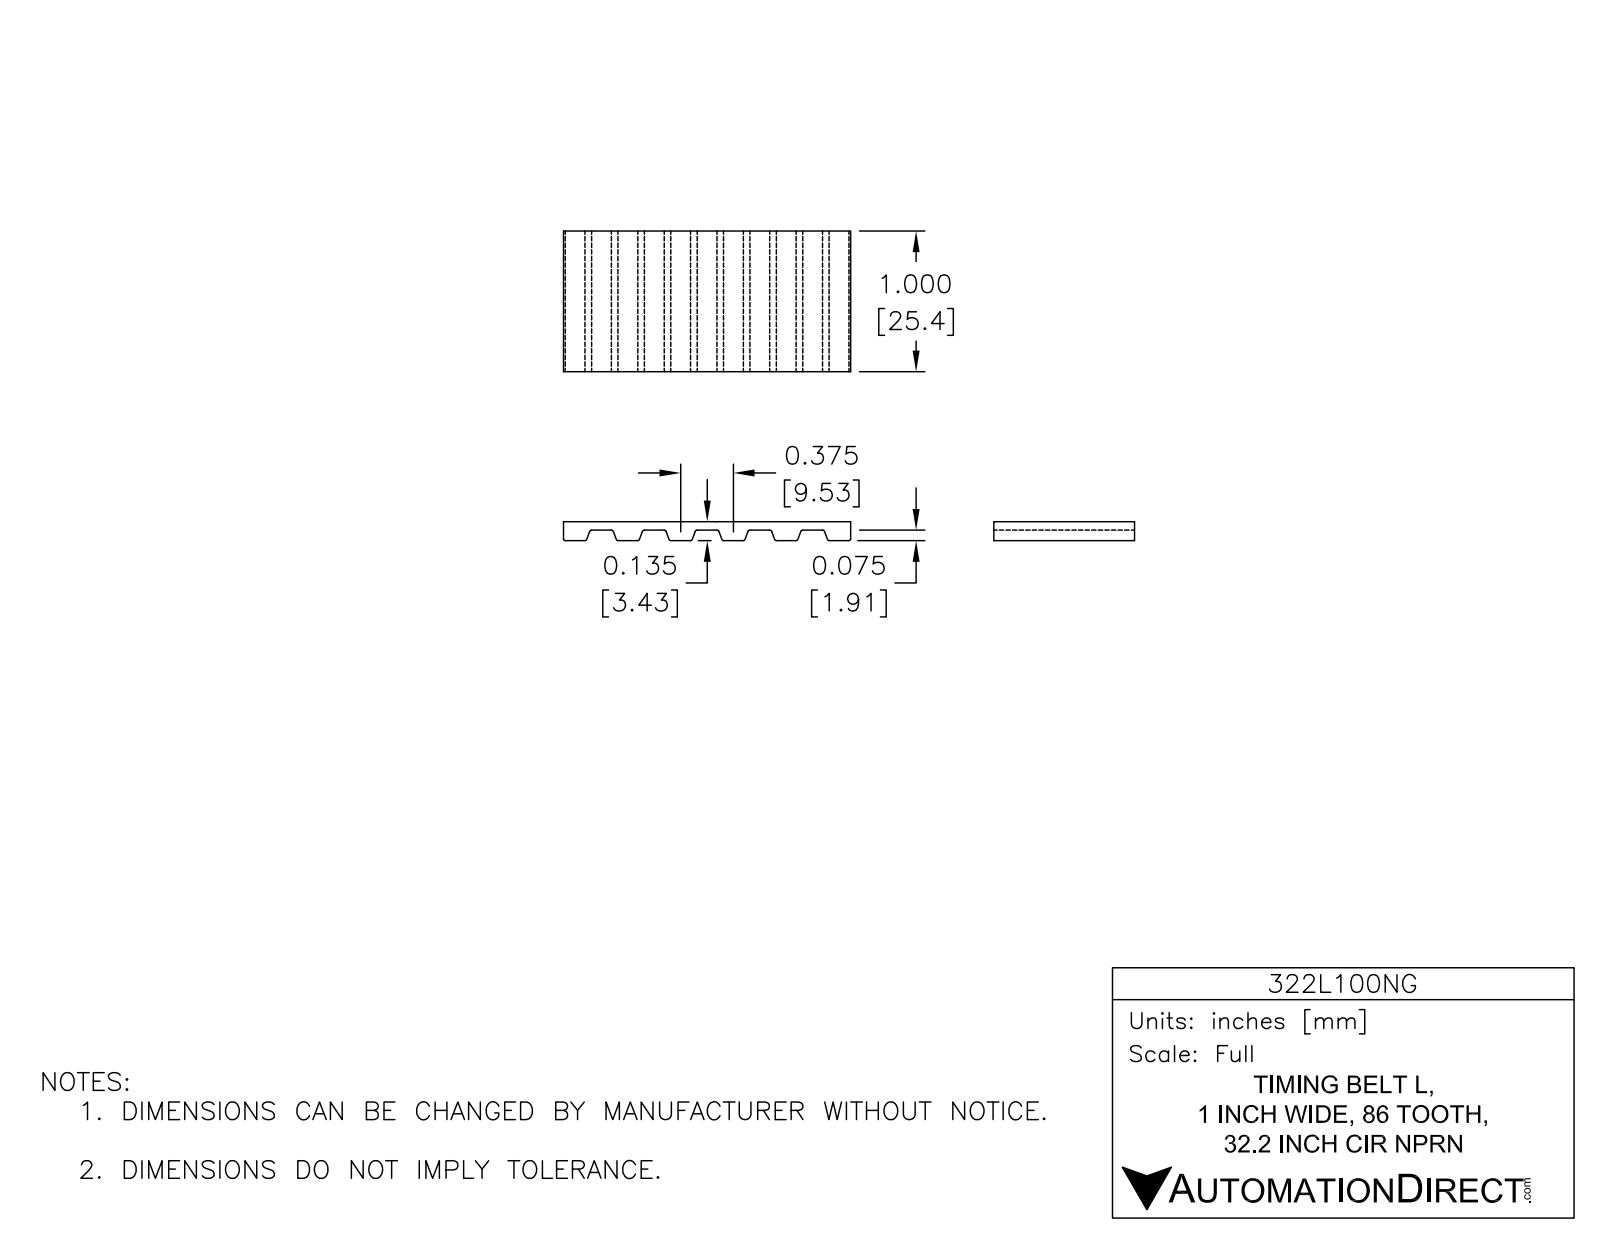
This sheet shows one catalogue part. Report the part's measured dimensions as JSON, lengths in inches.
{"part_name": "322L100NG", "step_written_by": "SolidWorks 2014 (AUTOMOTIVE_DESIGN)", "units": "inches", "bodies": {"solids": 1, "faces": 700, "planar": 320, "cylindrical": 380, "other": 0}, "overall_size": [14.413, 3, 1], "volume_in3": 2.918, "surface_area_in2": 77.62, "partial_cylinders_radius": [[0.02, 340], [1.435, 2], [1.5, 2]], "face_to_face_distances": [0.065, 2.935, 3, 2.87, 0.14, 2.86, 0.075, 2.795, 1, 2.72]}
